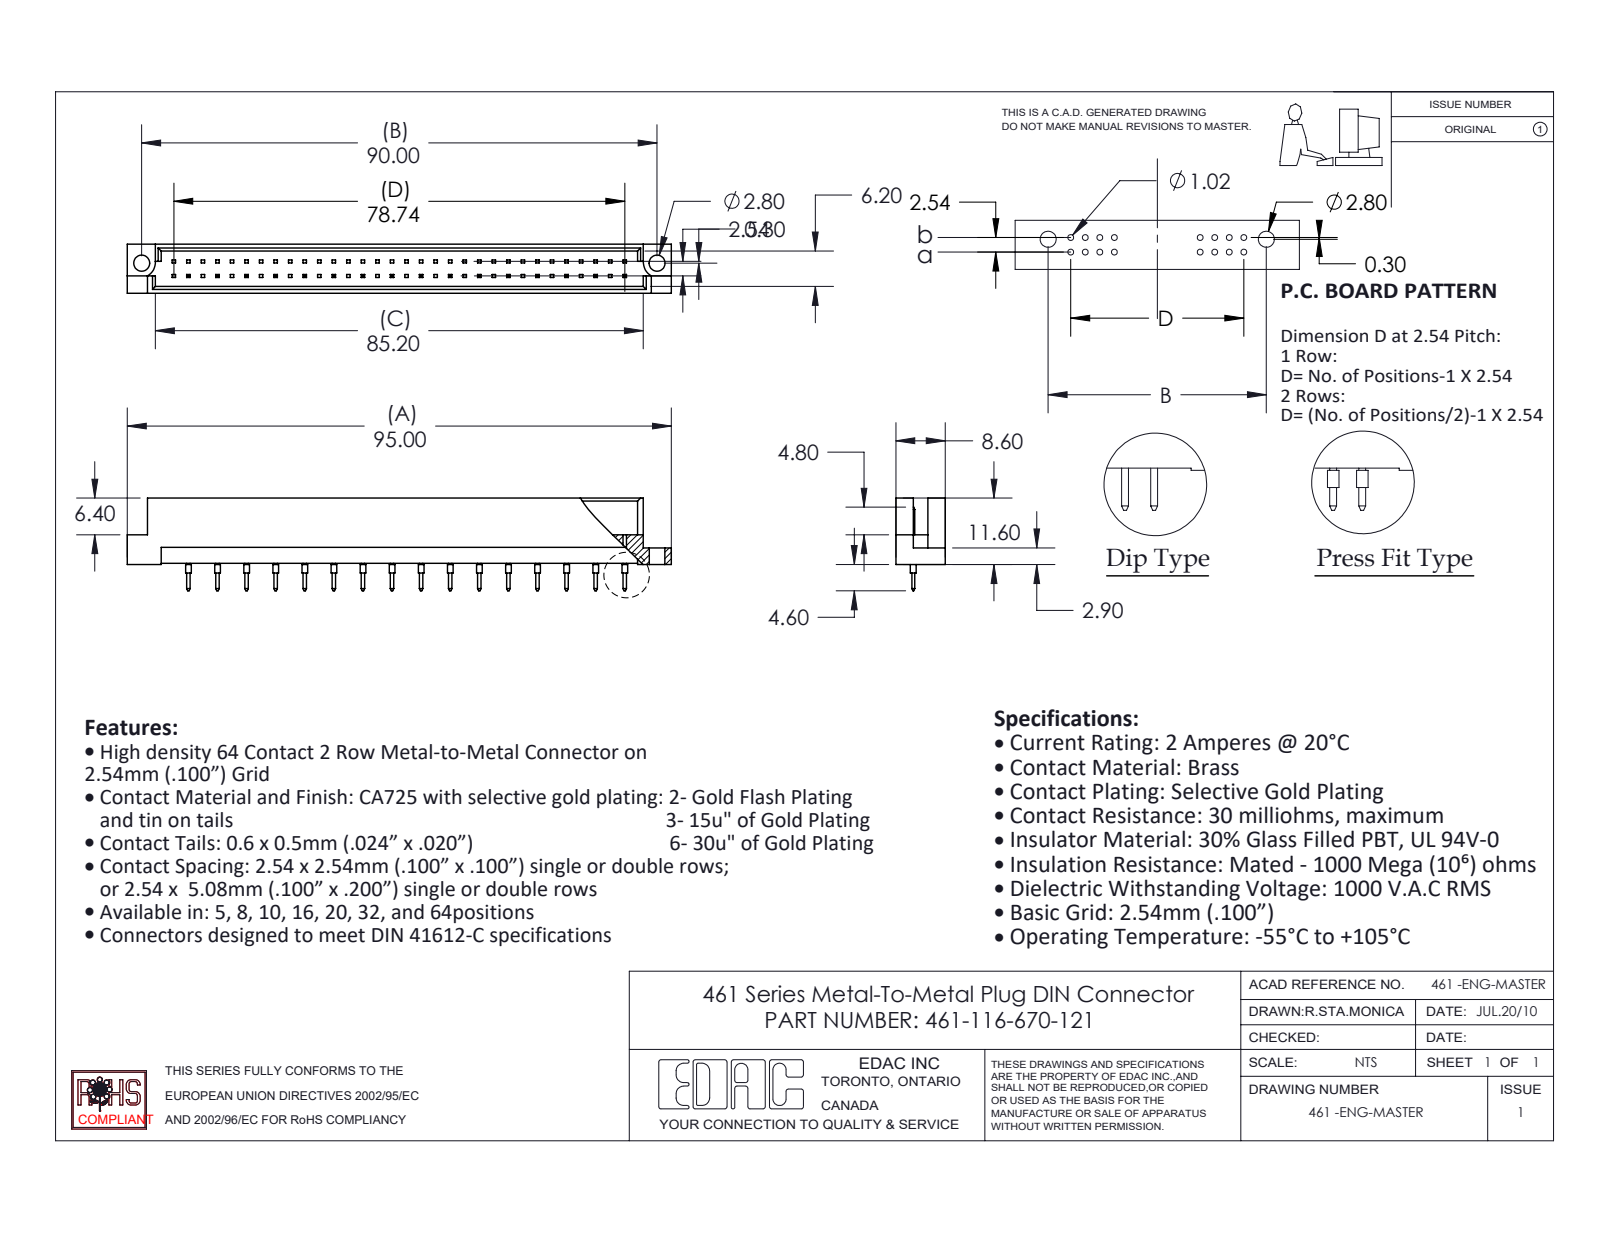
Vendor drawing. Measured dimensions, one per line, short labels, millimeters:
name: 461-290_70; 461 Part_64; 461-116-670-121
written by: SolidWorks 2020 (CONFIG_CONTROL_DESIGN)
unit: mm
bodies: 17 solids, 657 faces (618 planar, 39 cylindrical, 0 other)
size: 95 × 16.2 × 8.6
volume: 4 737 mm³; area: 6 218 mm²
holes: 2× ⌀2.8
bosses: 16× ⌀1
rounds: 2× R2.8
face distances: 1.2, 7.4, 8.6, 6.2, 5, 1.58, 3.28, 5.32, 2.08, 4.12
hole spacings: 90
